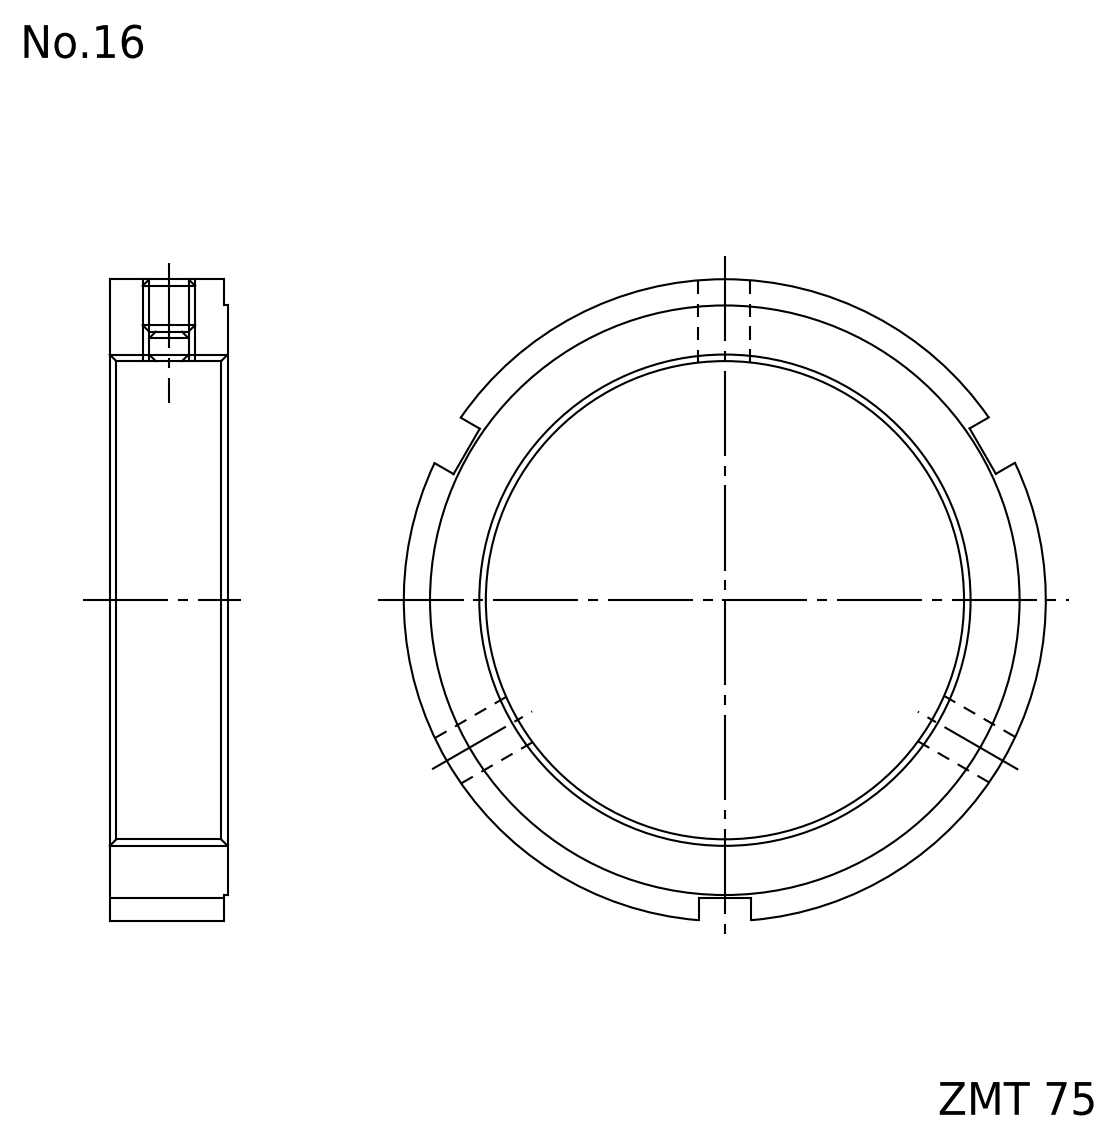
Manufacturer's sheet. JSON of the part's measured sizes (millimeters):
{"part_name": "FKD ZMT 75", "step_written_by": "Autodesk Inventor 2011 (AUTOMOTIVE_DESIGN)", "units": "millimeters", "bodies": {"solids": 1, "faces": 20, "planar": 12, "cylindrical": 8, "other": 0}, "overall_size": [98, 97.84, 18], "volume_mm3": 53016, "surface_area_mm2": 16718, "round_holes": [[6.65, 3], [75, 1]], "round_bosses_or_shafts": [[98, 1], [90, 1]], "face_to_face_distances": [18, 0.5, 17.5, 8]}
